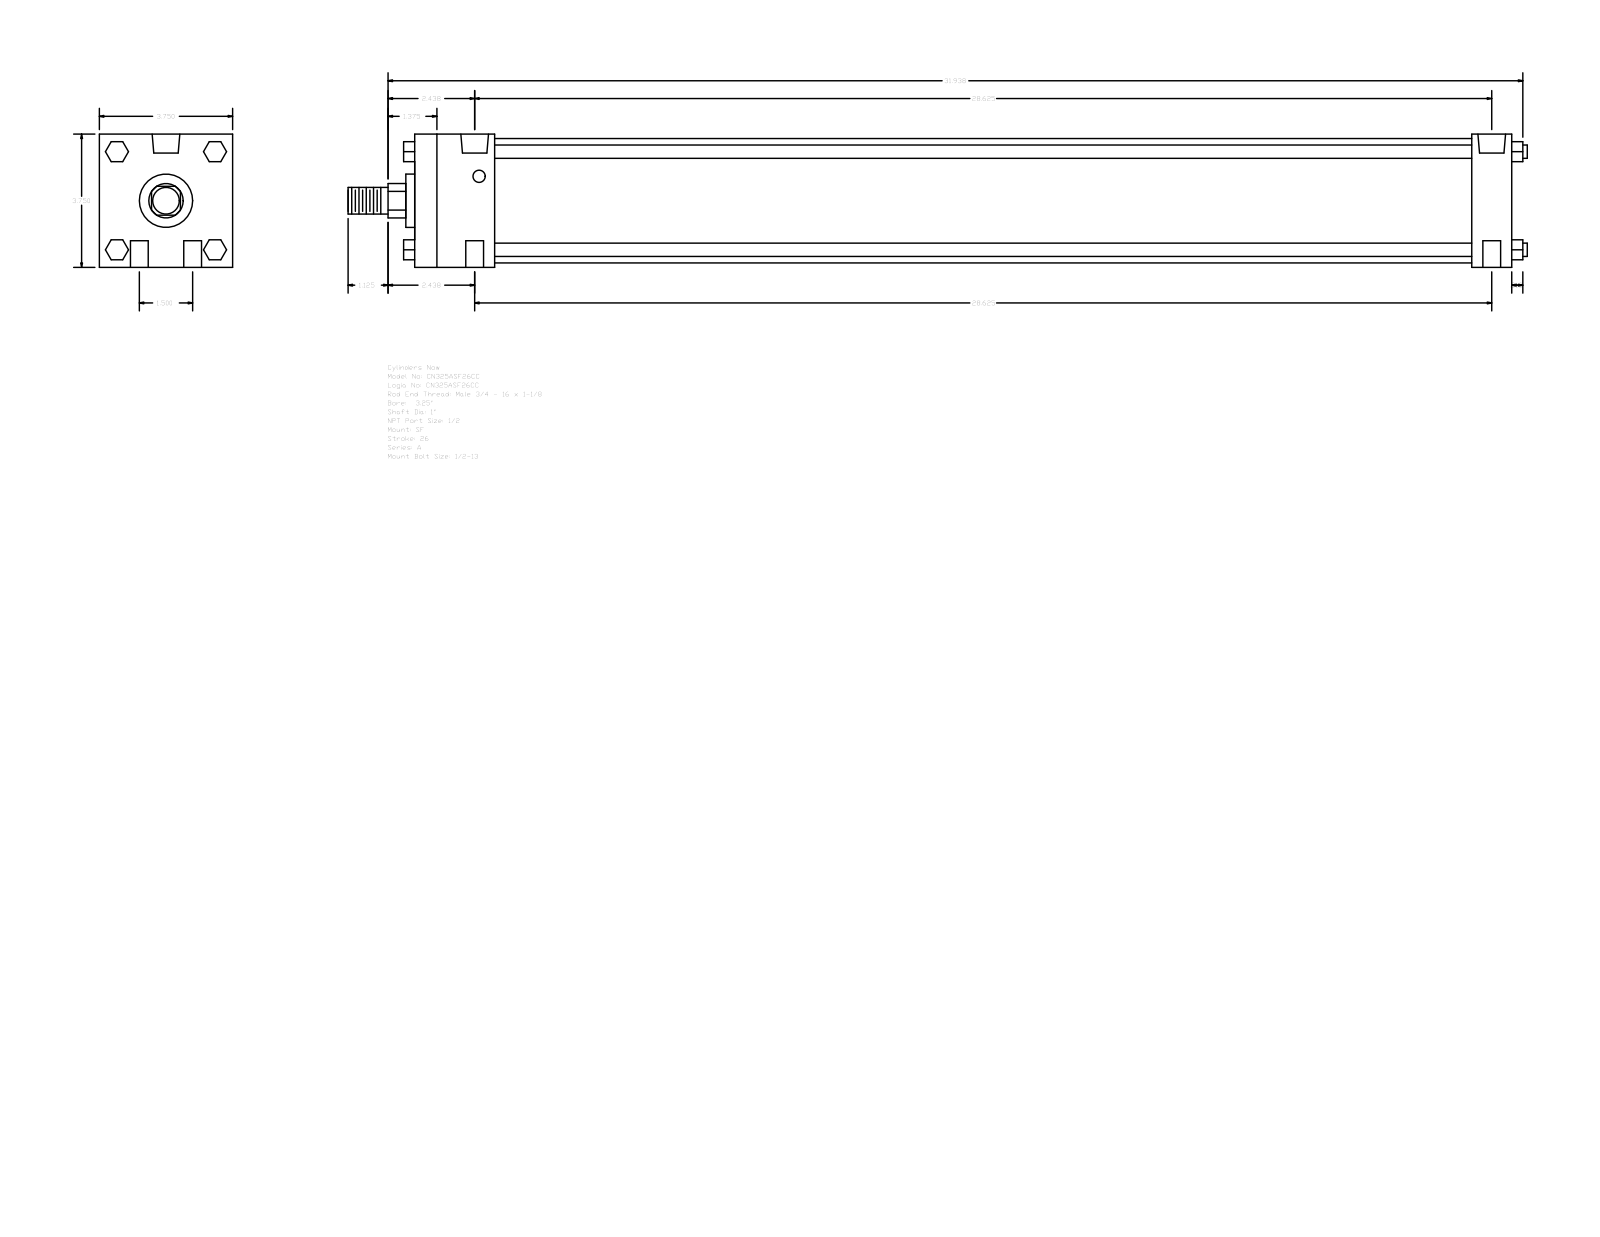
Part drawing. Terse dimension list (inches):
name: A_SF__0325_1
written by: GSSL Pune (CONFIG_CONTROL_DESIGN)
unit: in
bodies: 0 solids, 124 faces (94 planar, 30 cylindrical, 0 other)
size: 33.187 × 3.75 × 3.75
holes: 4× ⌀0.5, 2× ⌀0.344, 2× ⌀0.778
bosses: 4× ⌀0.375, 1× ⌀3.5, 1× ⌀1.5, 1× ⌀1, 1× ⌀0.75
rounds: 1× R0.484
face distances: 3.75, 30.875, 1.125, 29.75, 2.25, 27.5, 28.625, 0.562, 1.38, 2.39
hole spacings: 0.75, 28.635, 28.625, 1.5, 28.665, 28.375
